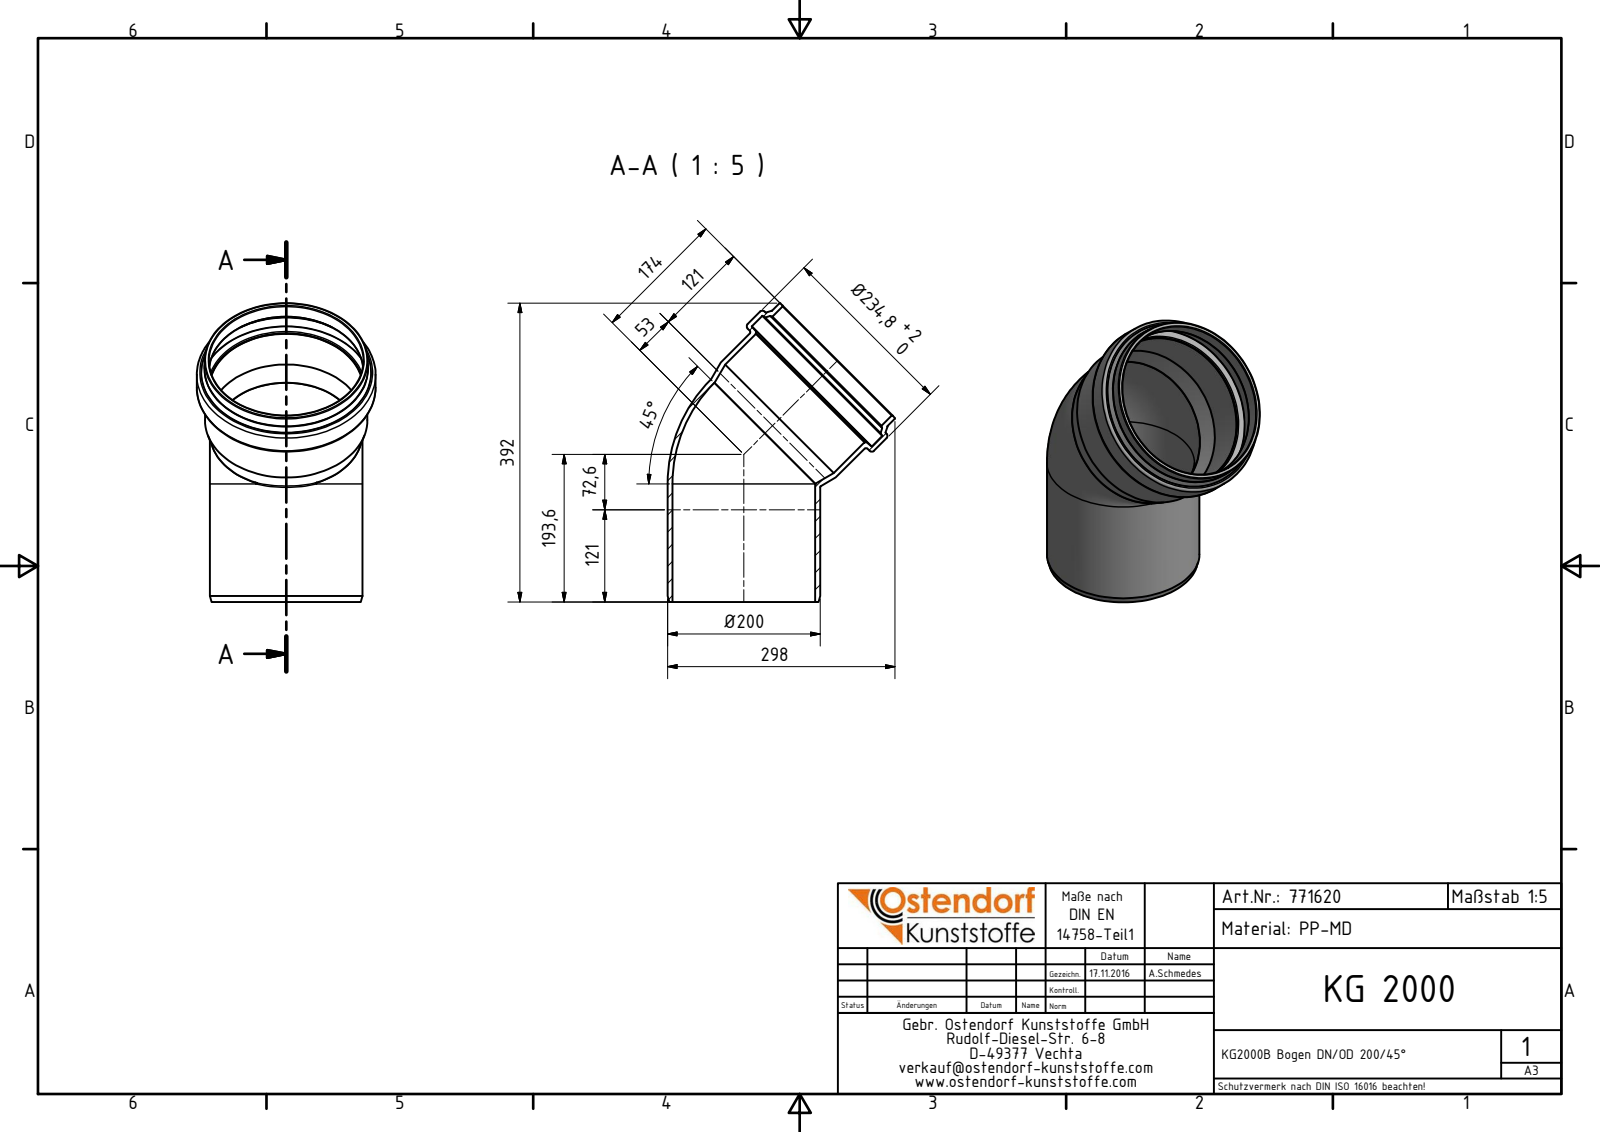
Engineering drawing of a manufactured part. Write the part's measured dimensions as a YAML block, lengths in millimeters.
part_name: "771620 KG2000B Bogen DN_OD 200_45°"
step_written_by: "Autodesk Inventor 2016 (AUTOMOTIVE_DESIGN)"
units: millimeters
bodies: {solids: 1, faces: 41, planar: 5, cylindrical: 11, other: 25}
overall_size: [392, 298.49, 234.8]
volume: 1430000
surface_area: 483863
round_holes:
  - {diameter: 187.2, count: 2}
  - {diameter: 202.5, count: 2}
  - {diameter: 201.5, count: 1}
  - {diameter: 223, count: 1}
round_bosses_or_shafts:
  - {diameter: 200.2, count: 2}
  - {diameter: 234.8, count: 1}
  - {diameter: 214.3, count: 1}
  - {diameter: 213.3, count: 1}
face_to_face_distances: [53.9, 31.6, 22.3, 2.89, 28.71, 51.01]
